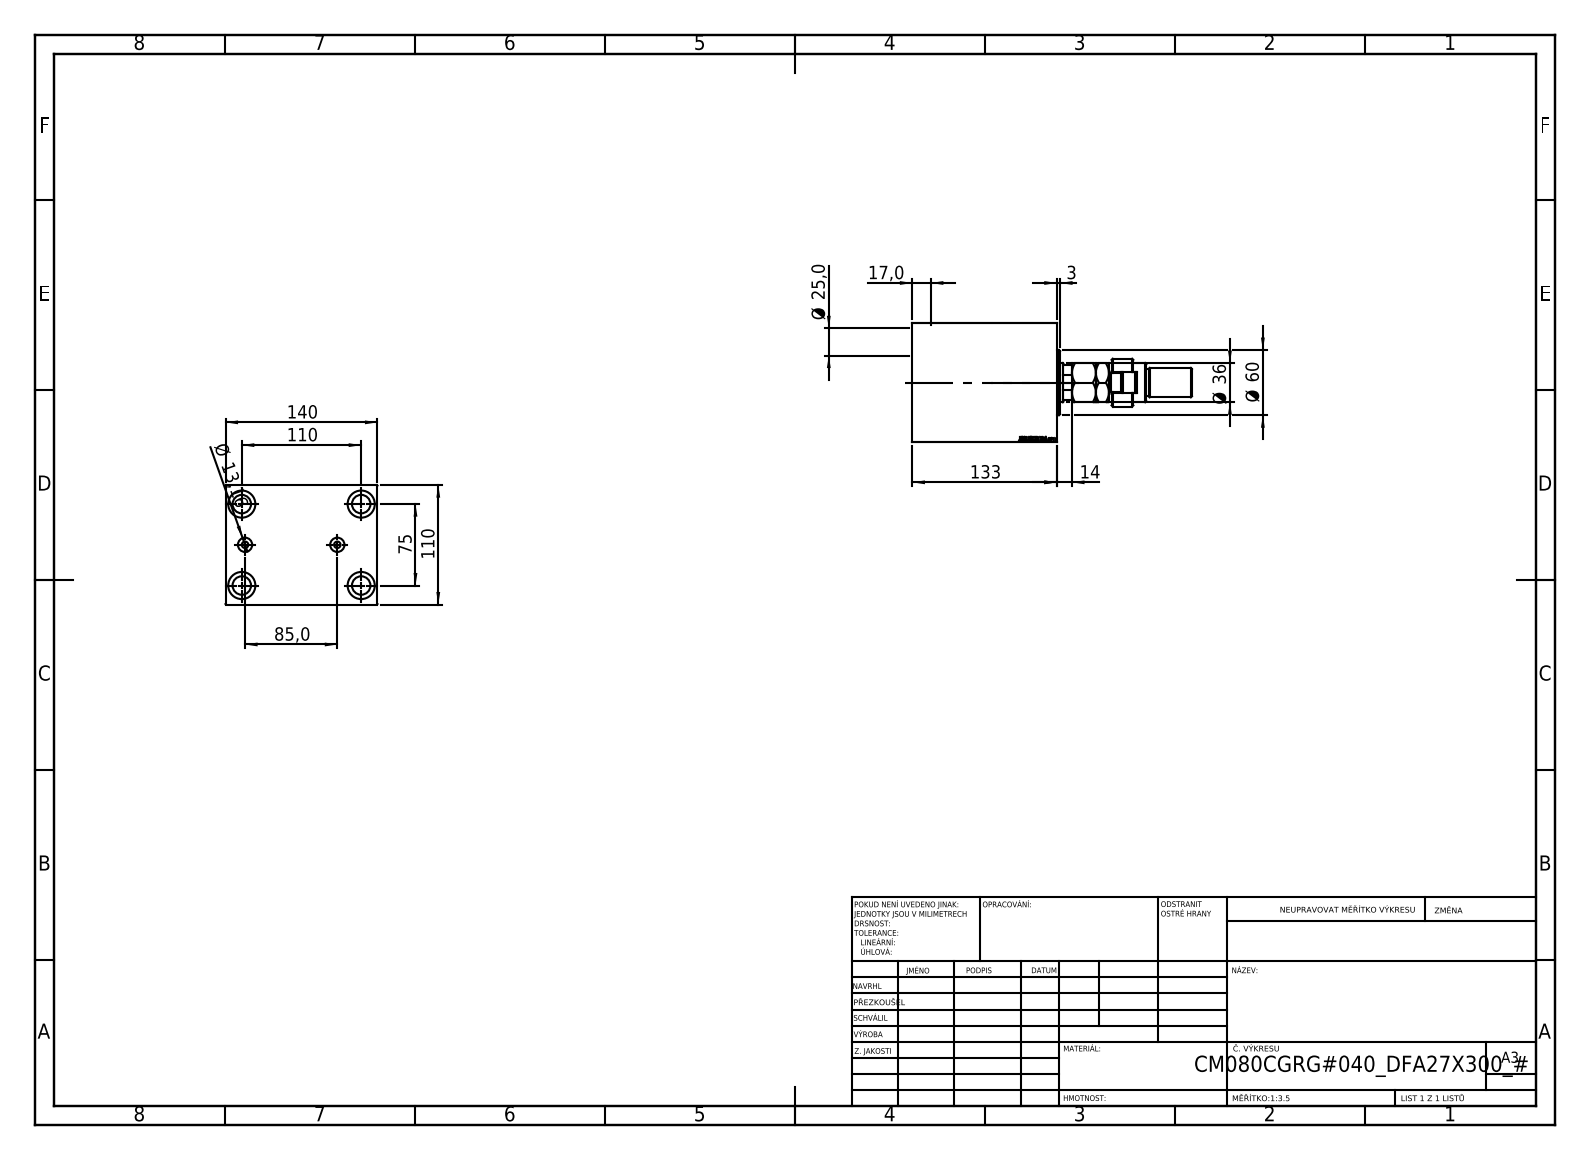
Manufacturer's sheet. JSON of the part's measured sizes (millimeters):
{"part_name": "FEMALE_PART_FOR_DFA; V450CM_C_VCP; MFA; V450CM_VC_B (+1 more)", "step_written_by": "SolidWorks 2019 (CONFIG_CONTROL_DESIGN)", "units": "millimeters", "bodies": {"solids": 5, "faces": 945, "planar": 436, "cylindrical": 71, "other": 438}, "overall_size": [257.5, 140, 110], "volume_mm3": 1824000, "surface_area_mm2": 230592, "round_holes": [[17, 4], [25, 4], [6, 2], [13.16, 2], [25.5, 1], [39.5, 1], [80, 1], [82, 1], [87, 1]], "round_bosses_or_shafts": [[60, 1], [44, 1], [36, 1], [28, 1], [27, 1], [25, 1], [18, 1]], "partial_cylinders_radius": [[9.5, 1], [15, 1], [17.5, 1]], "face_to_face_distances": [110, 140, 133, 112, 21, 14, 119, 54, 98, 40], "hole_center_spacings": [66.57, 37.62, 43.48, 75, 95.66, 110, 113.38, 133.14]}
